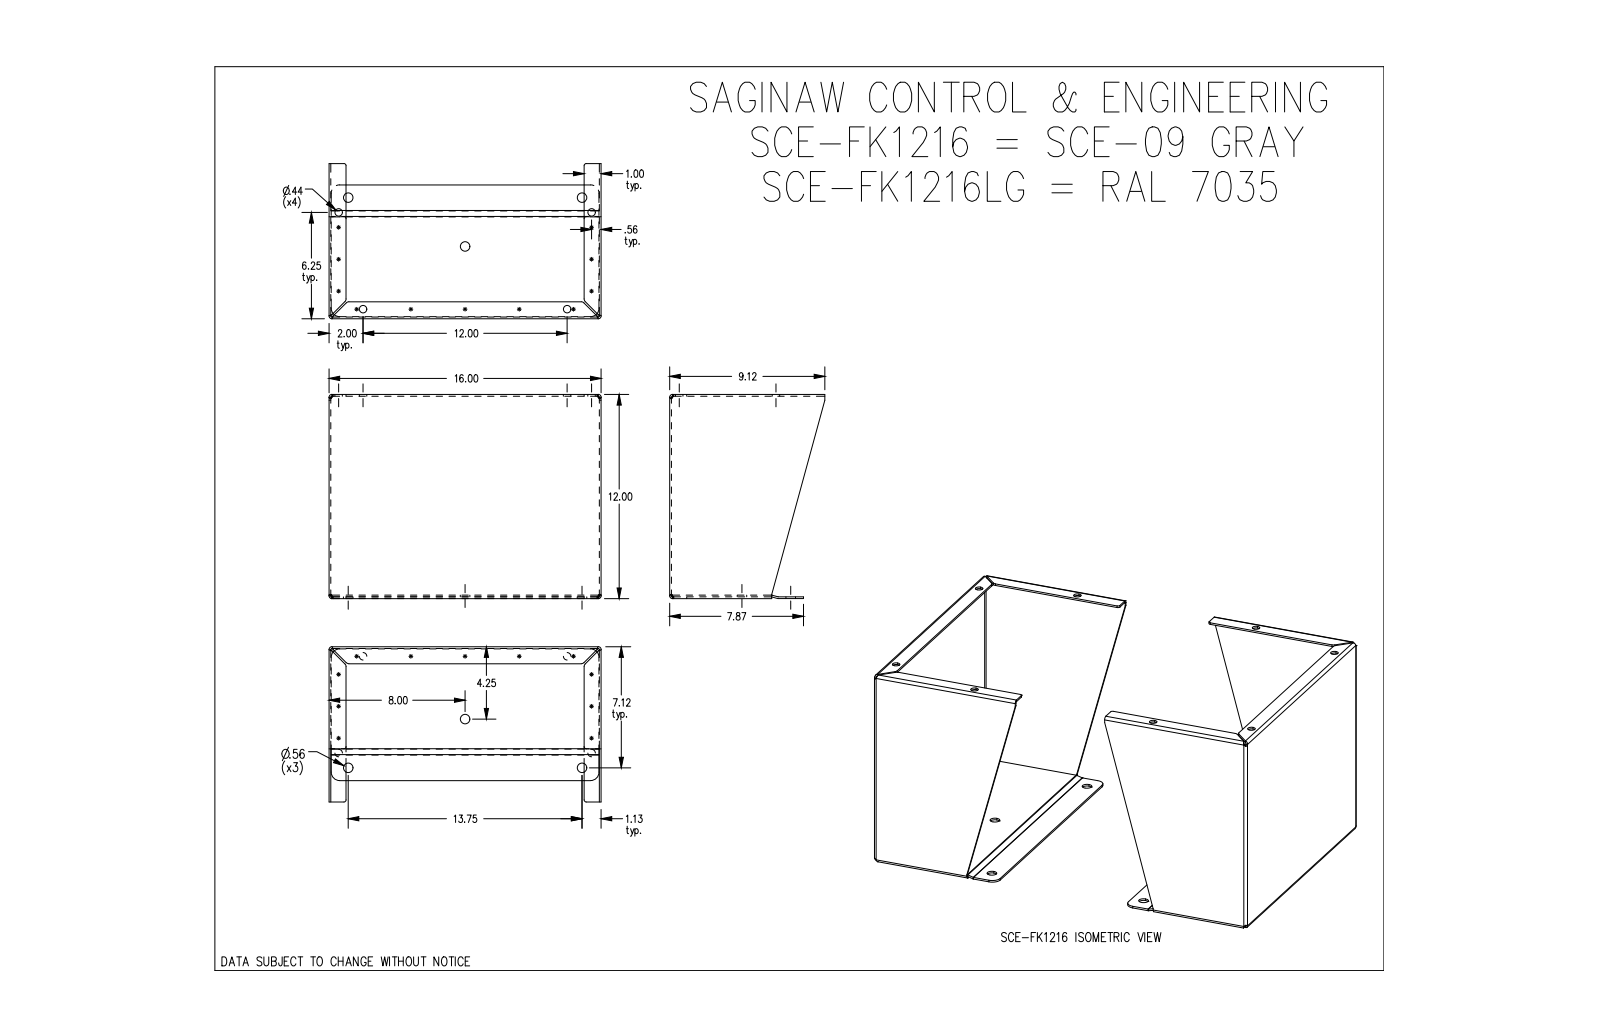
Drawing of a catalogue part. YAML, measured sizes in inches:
part_name: "SCE-FK1216"
step_written_by: "SolidWorks 2019 (CONFIG_CONTROL_DESIGN)"
units: inches
bodies: {solids: 4, faces: 214, planar: 96, cylindrical: 86, other: 32}
overall_size: [24, 16, 12]
volume: 112.1
surface_area: 2186
round_holes:
  - {diameter: 0.437, count: 8}
  - {diameter: 0.563, count: 6}
partial_cylinders:
  - {radius: 0.166, count: 16}
  - {radius: 0.062, count: 12}
  - {radius: 0.125, count: 8}
  - {radius: 0.22, count: 8}
  - {radius: 0.5, count: 8}
  - {radius: 0.063, count: 6}
face_to_face_distances: [0.104, 23.896, 15.896, 23.792, 24, 15.792, 16, 11.792, 11.896, 0.101]
hole_center_spacings: [1.035, 5.866, 6.614, 7.043, 7.449, 7.701, 10.646, 14.38]
